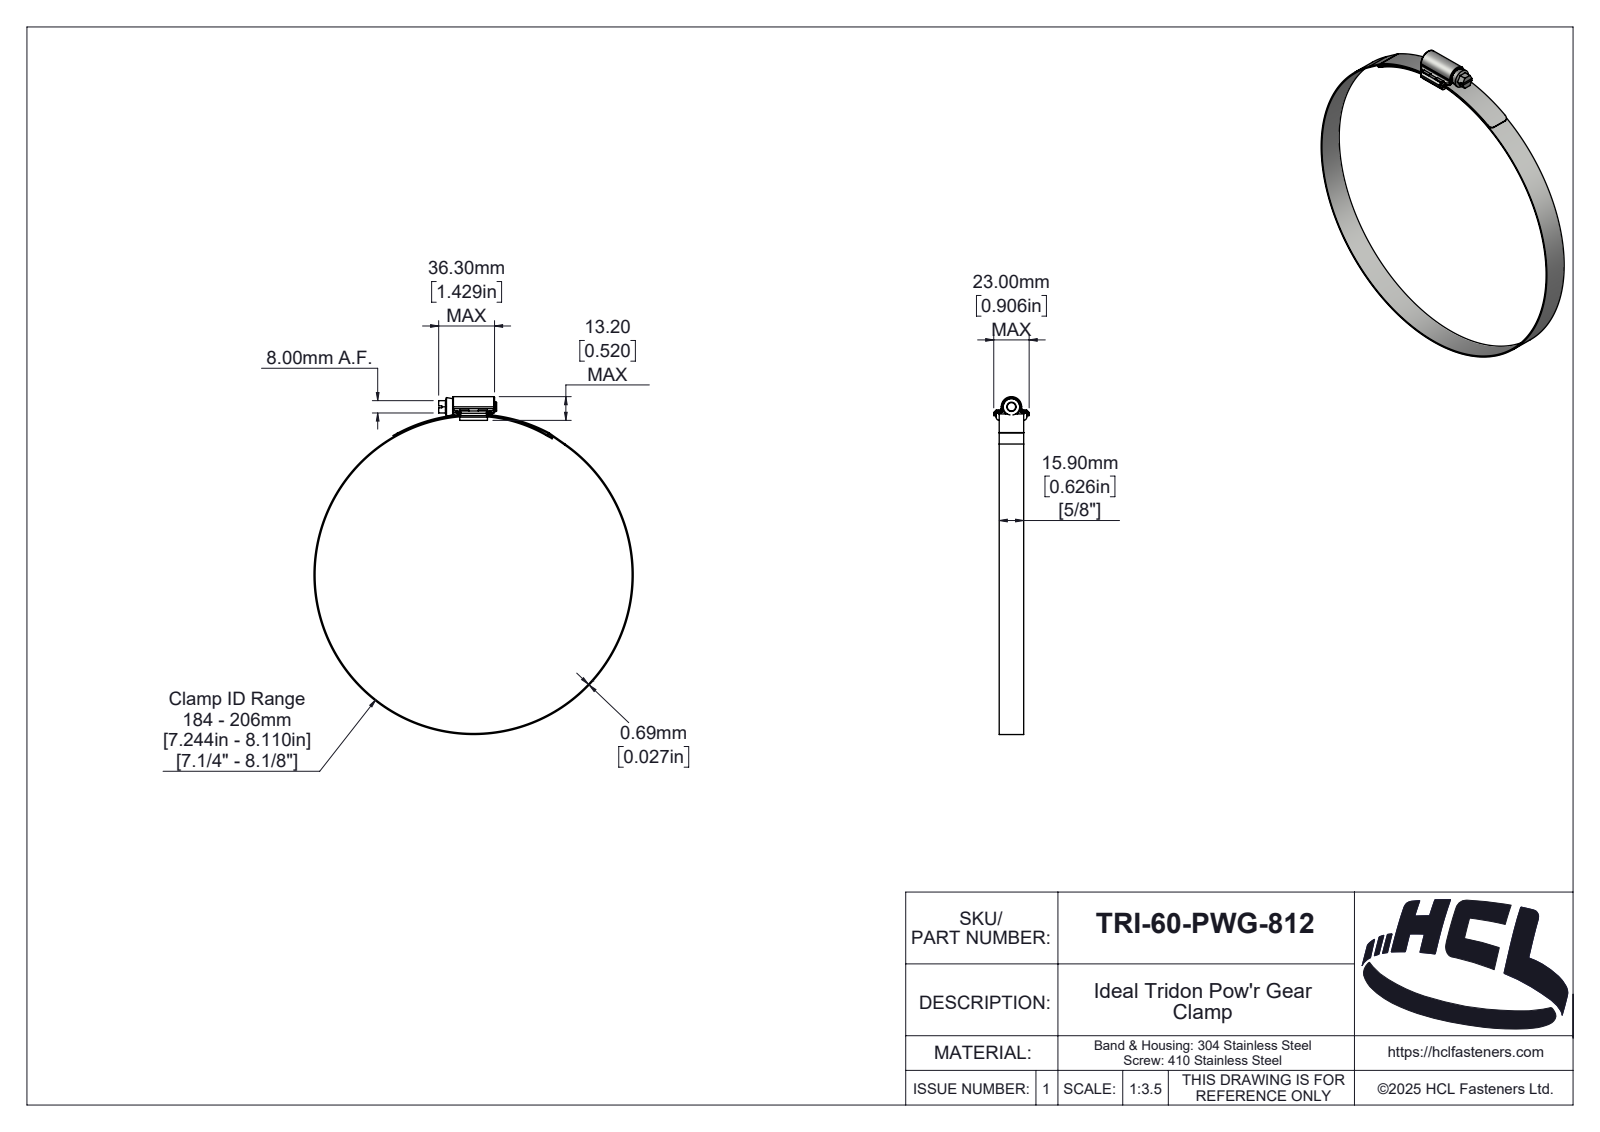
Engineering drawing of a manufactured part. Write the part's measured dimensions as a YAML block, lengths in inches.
part_name: "TRI-60-PWG-812"
step_written_by: "SolidWorks 2025 (AUTOMOTIVE_DESIGN)"
units: inches
bodies: {solids: 4, faces: 268, planar: 87, cylindrical: 102, other: 79}
overall_size: [8.637, 8.165, 0.906]
volume: 0.824
surface_area: 46.13
round_holes:
  - {diameter: 8.11, count: 1}
round_bosses_or_shafts:
  - {diameter: 8.165, count: 1}
  - {diameter: 0.421, count: 1}
  - {diameter: 0.236, count: 1}
partial_cylinders:
  - {radius: 0.039, count: 14}
  - {radius: 0.02, count: 4}
  - {radius: 0.059, count: 4}
  - {radius: 0.079, count: 3}
  - {radius: 0.004, count: 2}
  - {radius: 0.083, count: 2}
  - {radius: 0.118, count: 2}
  - {radius: 0.018, count: 1}
face_to_face_distances: [0.626, 0.079, 0.027, 0.705, 0.193, 0.047, 0.179, 0.132, 0.604, 0.1]
